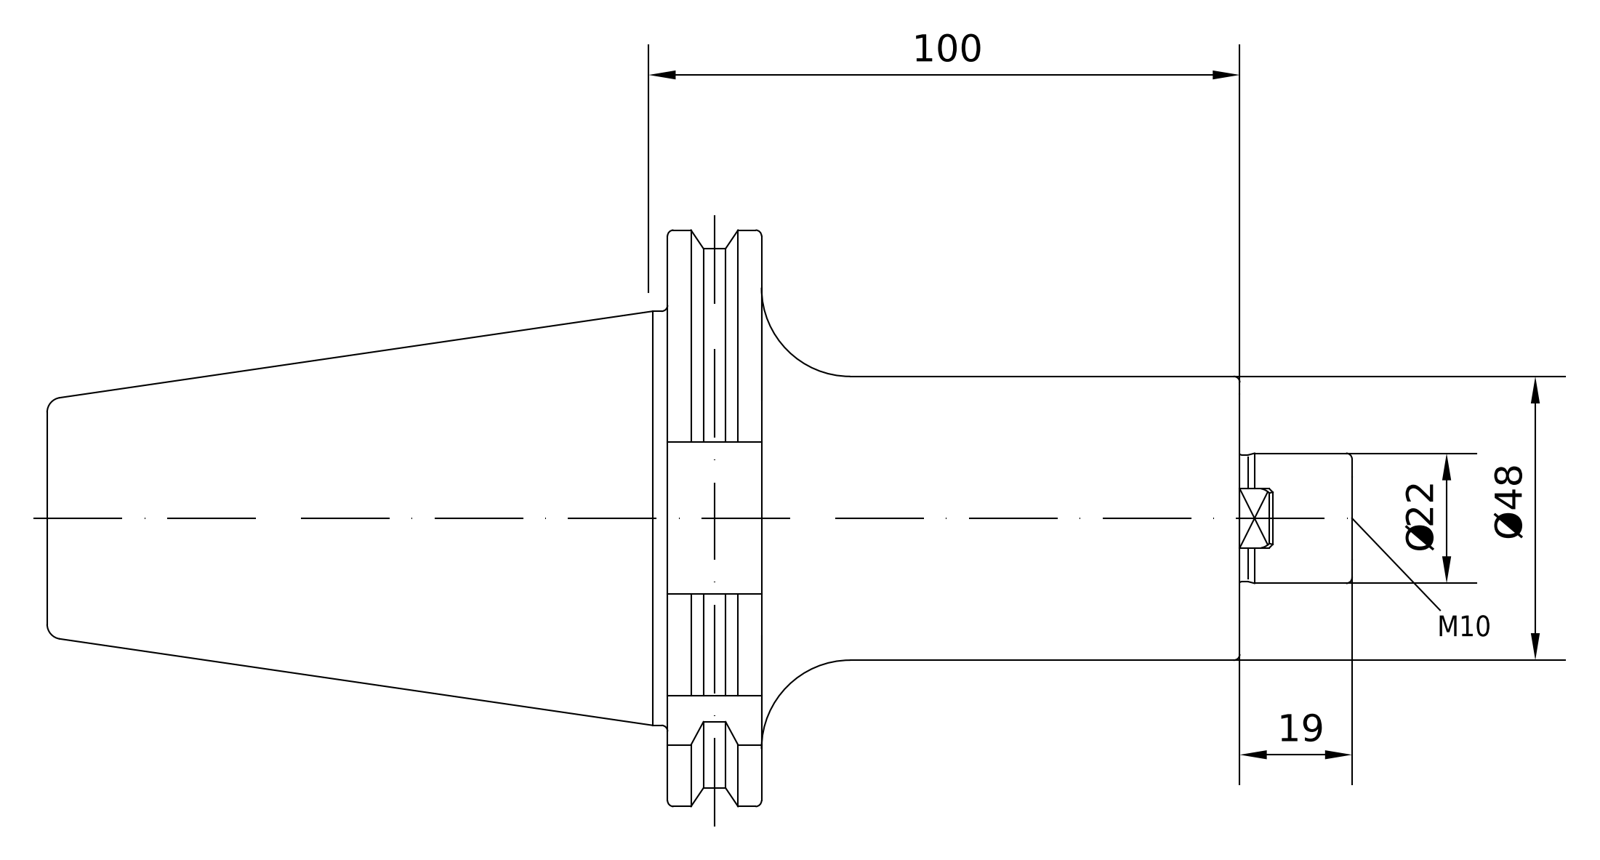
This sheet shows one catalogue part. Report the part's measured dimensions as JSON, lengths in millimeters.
{"part_name": "50-351-22", "step_written_by": "PRO/ENGINEER BY PARAMETRIC TECHNOLOGY CORPORATION, 2010430 (CONFIG_CONTROL_DESIGN)", "units": "millimeters", "bodies": {"solids": 1, "faces": 111, "planar": 33, "cylindrical": 28, "other": 50}, "overall_size": [220.6, 97.47, 94], "volume_mm3": 500652, "surface_area_mm2": 57176, "round_holes": [[8.5, 1], [10, 1], [20.75, 1], [25.01, 1], [25.7, 1]], "round_bosses_or_shafts": [[91, 1], [69.15, 1], [48, 1], [24.01, 1], [22, 1]], "partial_cylinders_radius": [[1.75, 1], [48.74, 1]], "face_to_face_distances": [15.85, 96.8, 80.95, 72.8, 104.8, 120.65, 201.6, 25.8, 220.6, 115.8]}
